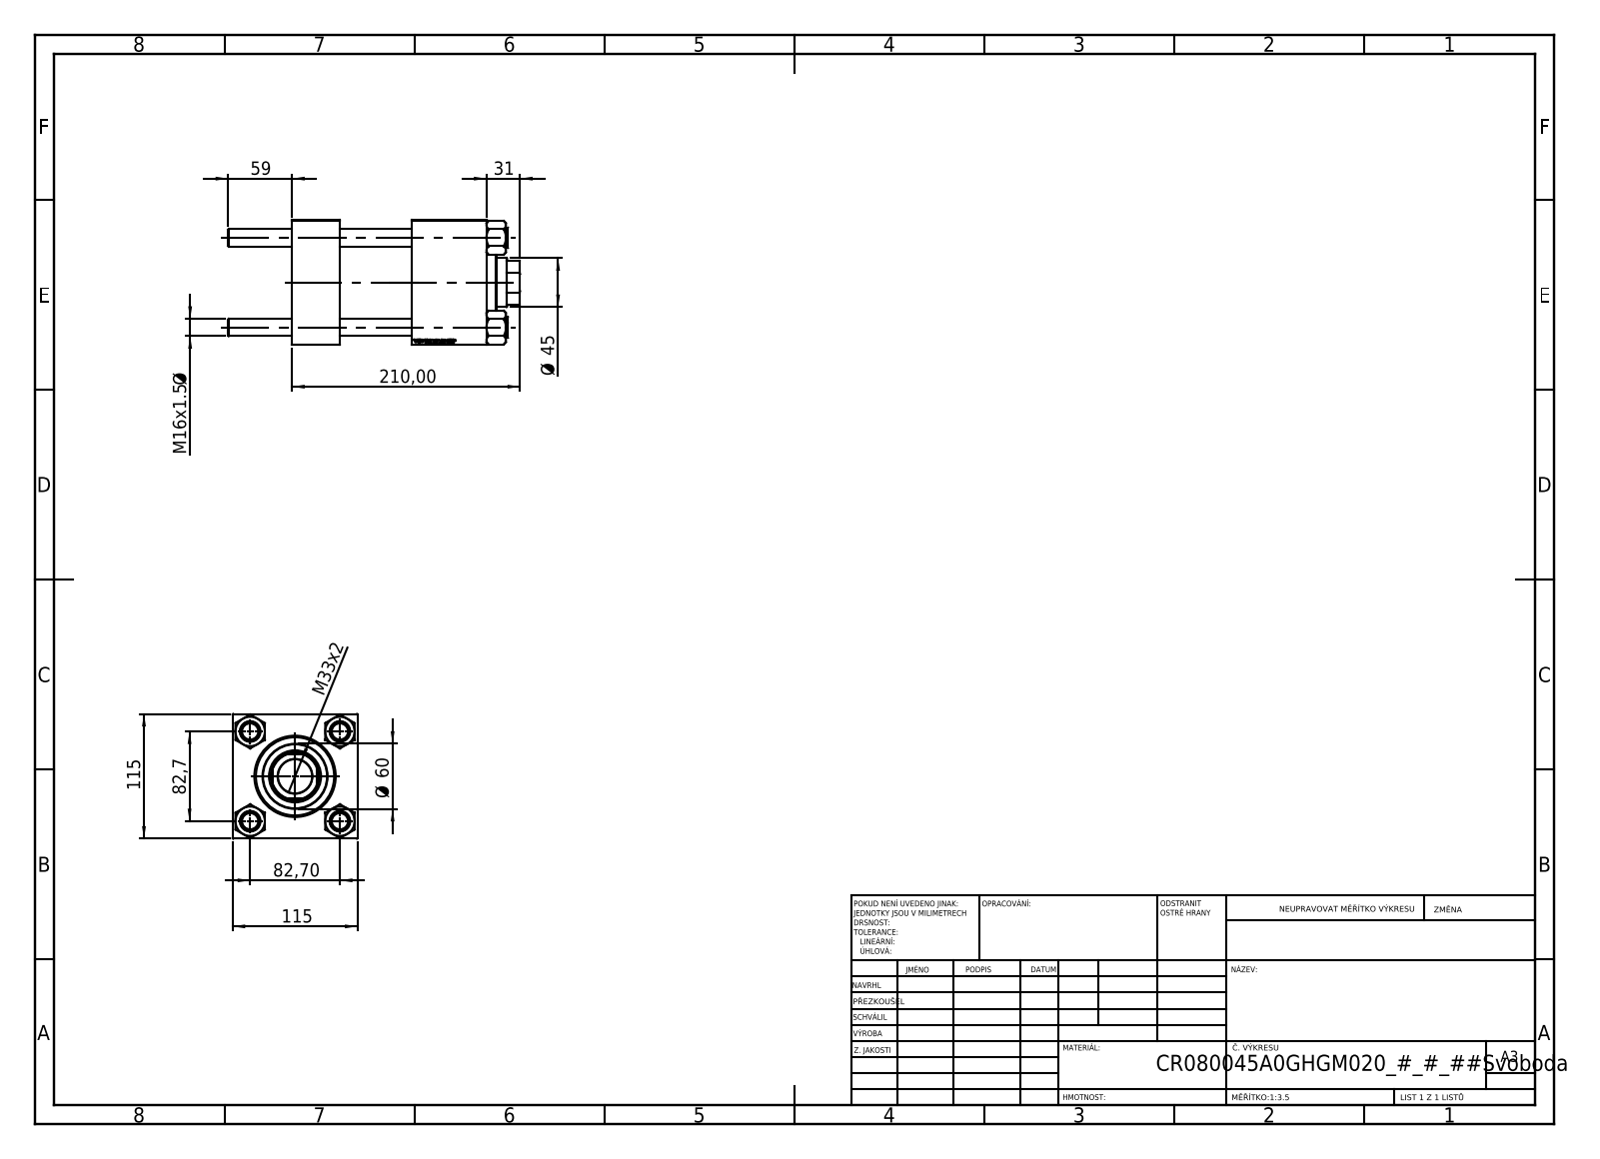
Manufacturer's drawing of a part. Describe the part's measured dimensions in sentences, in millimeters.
The part is named "CR025_012_A_0_G_A_G_M_020_+#_##_TYCINKA; V215_VC_A; NUT_M5; V215CR_VCP (+1 more)". Its 3-D file was written by "SolidWorks 2019 (CONFIG_CONTROL_DESIGN)". It is 11 solids with 1182 faces: 568 planar, 78 cylindrical and 536 other. Overall it measures 269 by 115 by 115 millimeters. Its volume is 1 899 000 cubic millimeters and its surface area 300 037 square millimeters. Round holes: 4 of diameter 16, 2 of diameter 7, 2 of diameter 26.44, 2 of diameter 35, 1 of diameter 31.5, 1 of diameter 45, 1 of diameter 48, 1 of diameter 61, 1 of diameter 72, 1 of diameter 80. Round bosses or shafts: 4 of diameter 19, 1 of diameter 86, 1 of diameter 60. Partial cylindrical surfaces (rounded edges, fillets, slot ends): 1 of radius 22. The main face-to-face distances are 115, 44, 179, 135, 110, 66, 69, 20, 89, 150.3. The hole center spacings are 58.48, 82.7, 116.96, 111.
